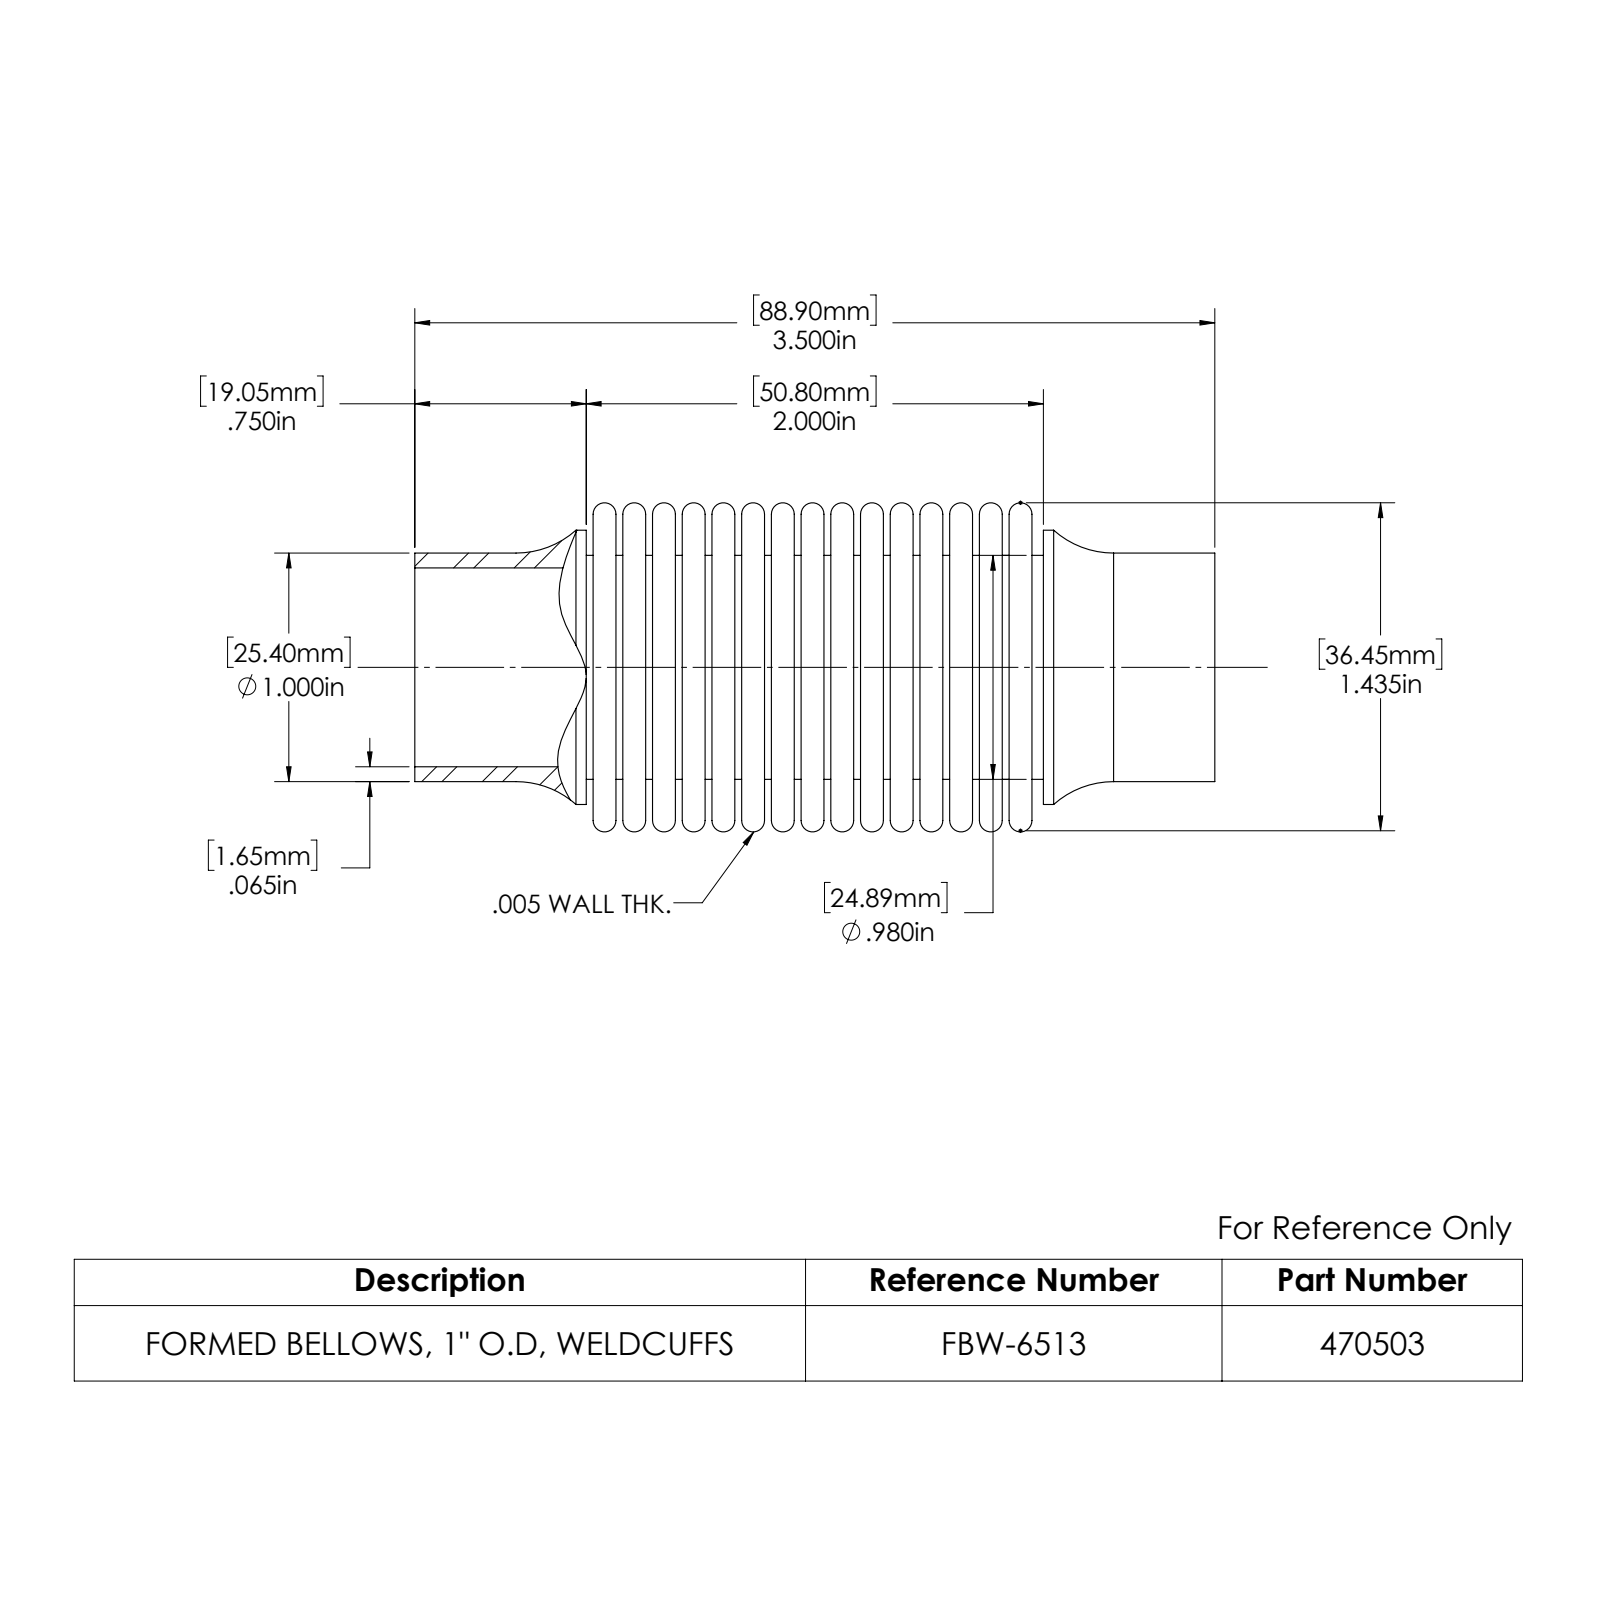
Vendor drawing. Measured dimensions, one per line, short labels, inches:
name: 470503
written by: SolidWorks 2022 (AUTOMOTIVE_DESIGN)
unit: in
bodies: 1 solid, 218 faces (70 planar, 84 cylindrical, 64 other)
size: 3.5 × 1.44 × 1.44
volume: 0.506 in³; area: 75.46 in²
holes: 1× ⌀0.87, 1× ⌀0.97, 1× ⌀1.19
bosses: 1× ⌀1.2, 1× ⌀1, 1× ⌀0.99, 1× ⌀0.98
face distances: 0.13, 0.65, 0.26, 0.52, 0.78, 0.91, 0.39, 0.39, 1.3, 1.17
